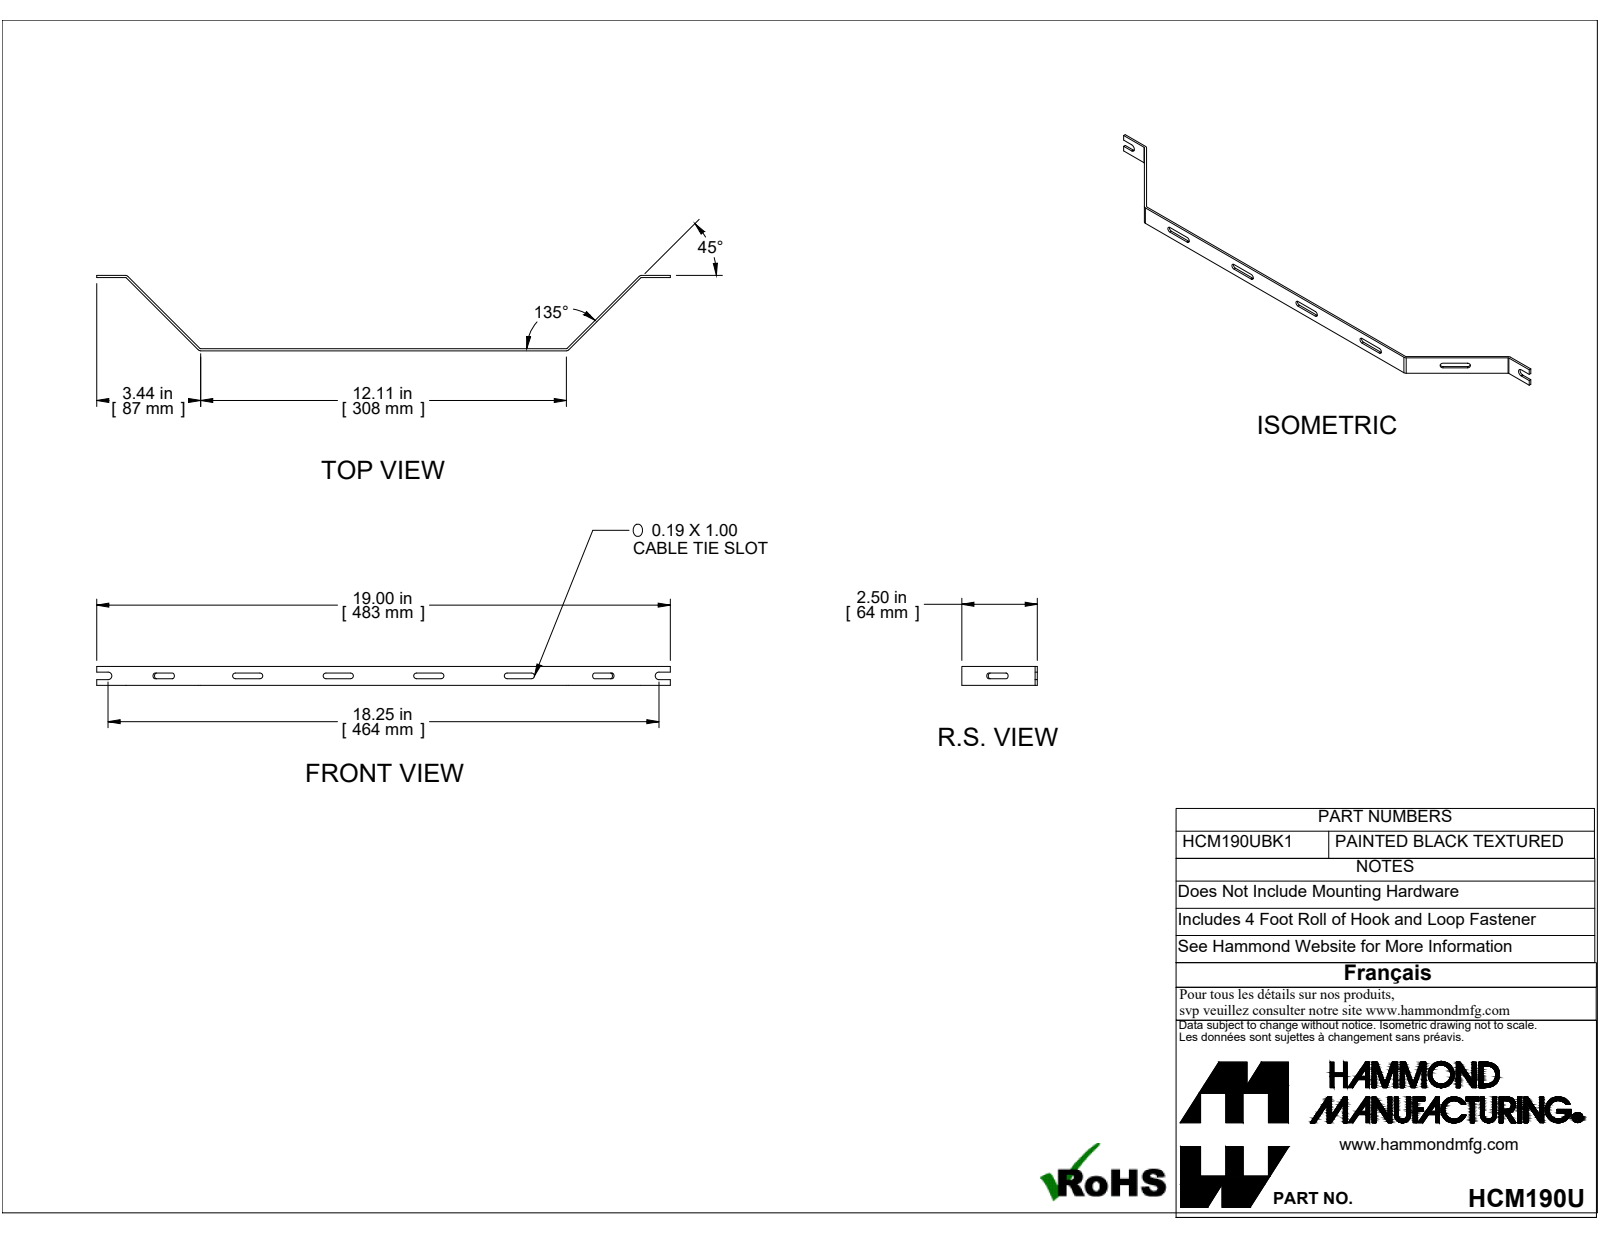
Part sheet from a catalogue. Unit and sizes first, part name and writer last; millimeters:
Units: millimetres
Overall size (bounding box): 482.6 × 63.5 × 15.88
Partial cylindrical surfaces — rounded edges, fillets, slot ends (radius × count): R2.39 ×12, R0.91 ×4, R2.74 ×4, R3.17 ×2
Main face-to-face distances: 1.83, 61.67, 15.88, 59.84, 63.5, 5.55, 10.33, 4.78, 4.77, 11.11
Volume: 13 929 mm³ · Surface area: 17 942 mm²
Bodies: 1 solid, 54 faces (32 planar, 22 cylindrical, 0 other)
STEP written by: Unknown (AUTOMOTIVE_DESIGN)
